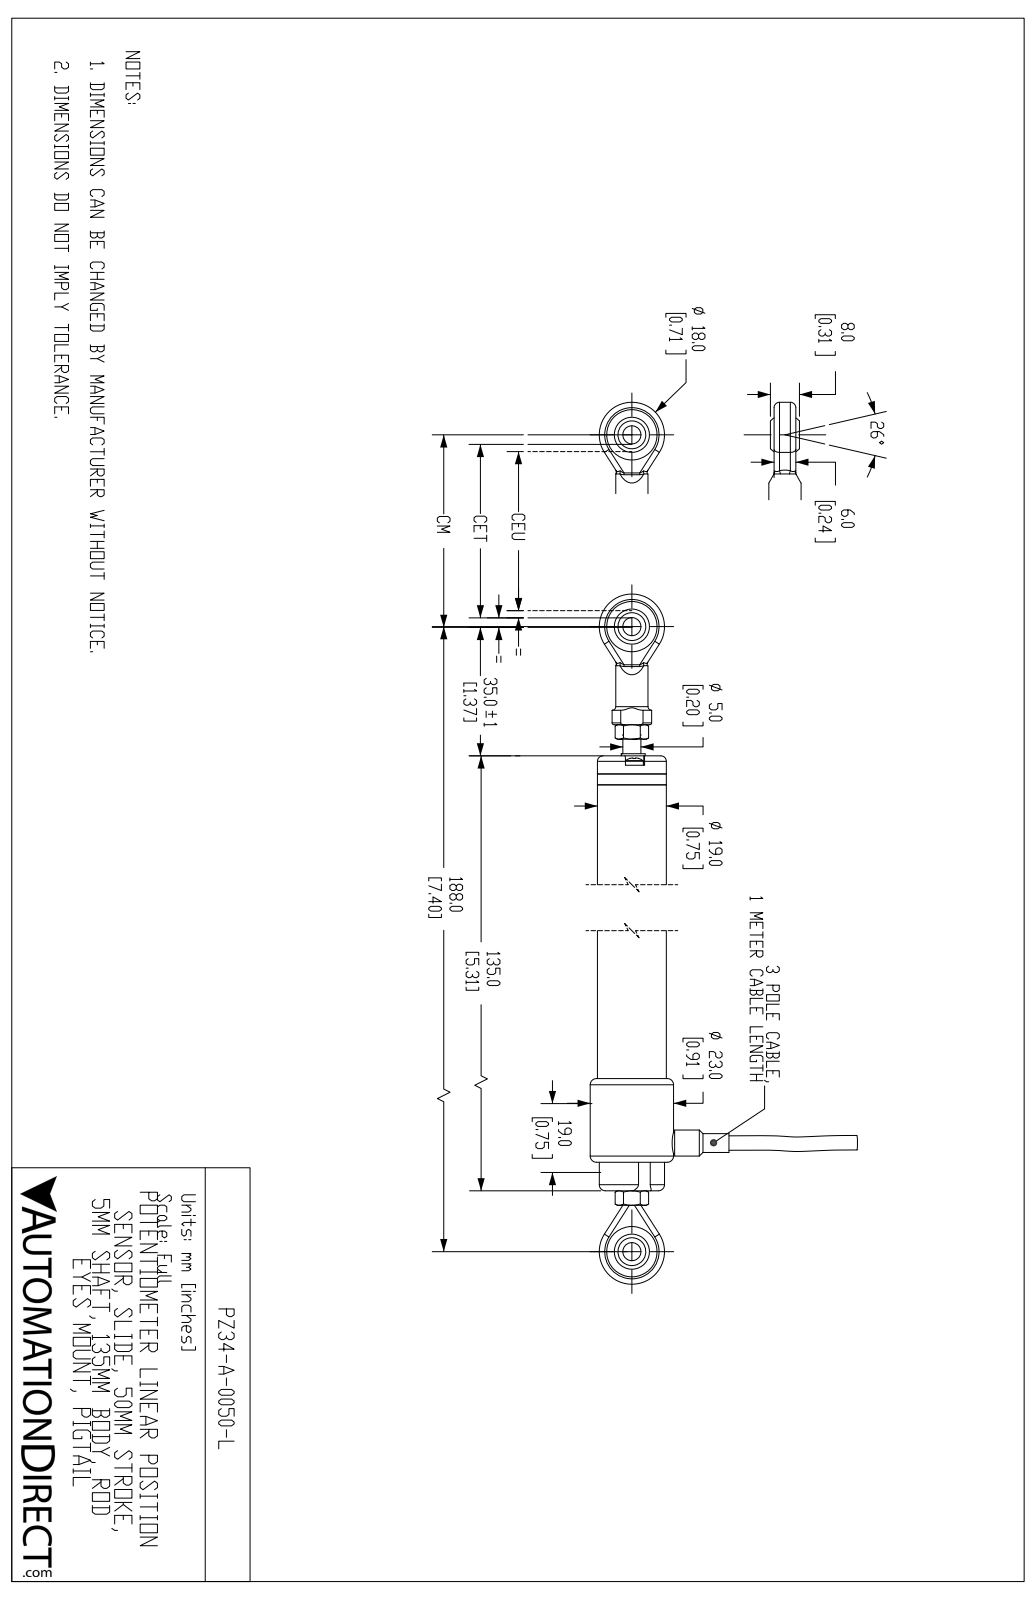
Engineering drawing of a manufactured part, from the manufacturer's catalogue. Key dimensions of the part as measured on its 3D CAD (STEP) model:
Part name (STEP PRODUCT): PZ34-A-0050-L
STEP written by: SolidWorks 2019 (AUTOMOTIVE_DESIGN)
Units: inches
Bodies: 18 solids, 916 faces (334 planar, 198 cylindrical, 384 other)
Overall size (bounding box): 8.091 × 2.904 × 0.906
Volume: 3.045 in³ · Surface area: 35.07 in²
Round holes (diameter × count): ⌀0.079 ×4, ⌀0.114 ×4, ⌀0.197 ×2, ⌀0.209 ×2, ⌀0.547 ×2, ⌀0.138 ×1, ⌀0.165 ×1, ⌀0.24 ×1, ⌀0.354 ×1, ⌀0.75 ×1
Round bosses / shafts (diameter × count): ⌀0.197 ×5, ⌀0.098 ×4, ⌀0.906 ×1, ⌀0.748 ×1, ⌀0.709 ×1, ⌀0.35 ×1, ⌀0.283 ×1, ⌀0.236 ×1
Partial cylindrical surfaces — rounded edges, fillets, slot ends (radius × count): R0.059 ×8, R0.01 ×4, R0.02 ×2, R0.039 ×2, R0.104 ×2, R0.354 ×2, R0.017 ×1, R0.063 ×1
Main face-to-face distances: 4.409, 4.291, 0.118, 0.315, 0.224, 0.213, 0.217, 0.051, 0.039, 0.264
Hole centre spacings: 0.269, 0.082, 0.532, 0.539, 7.382
